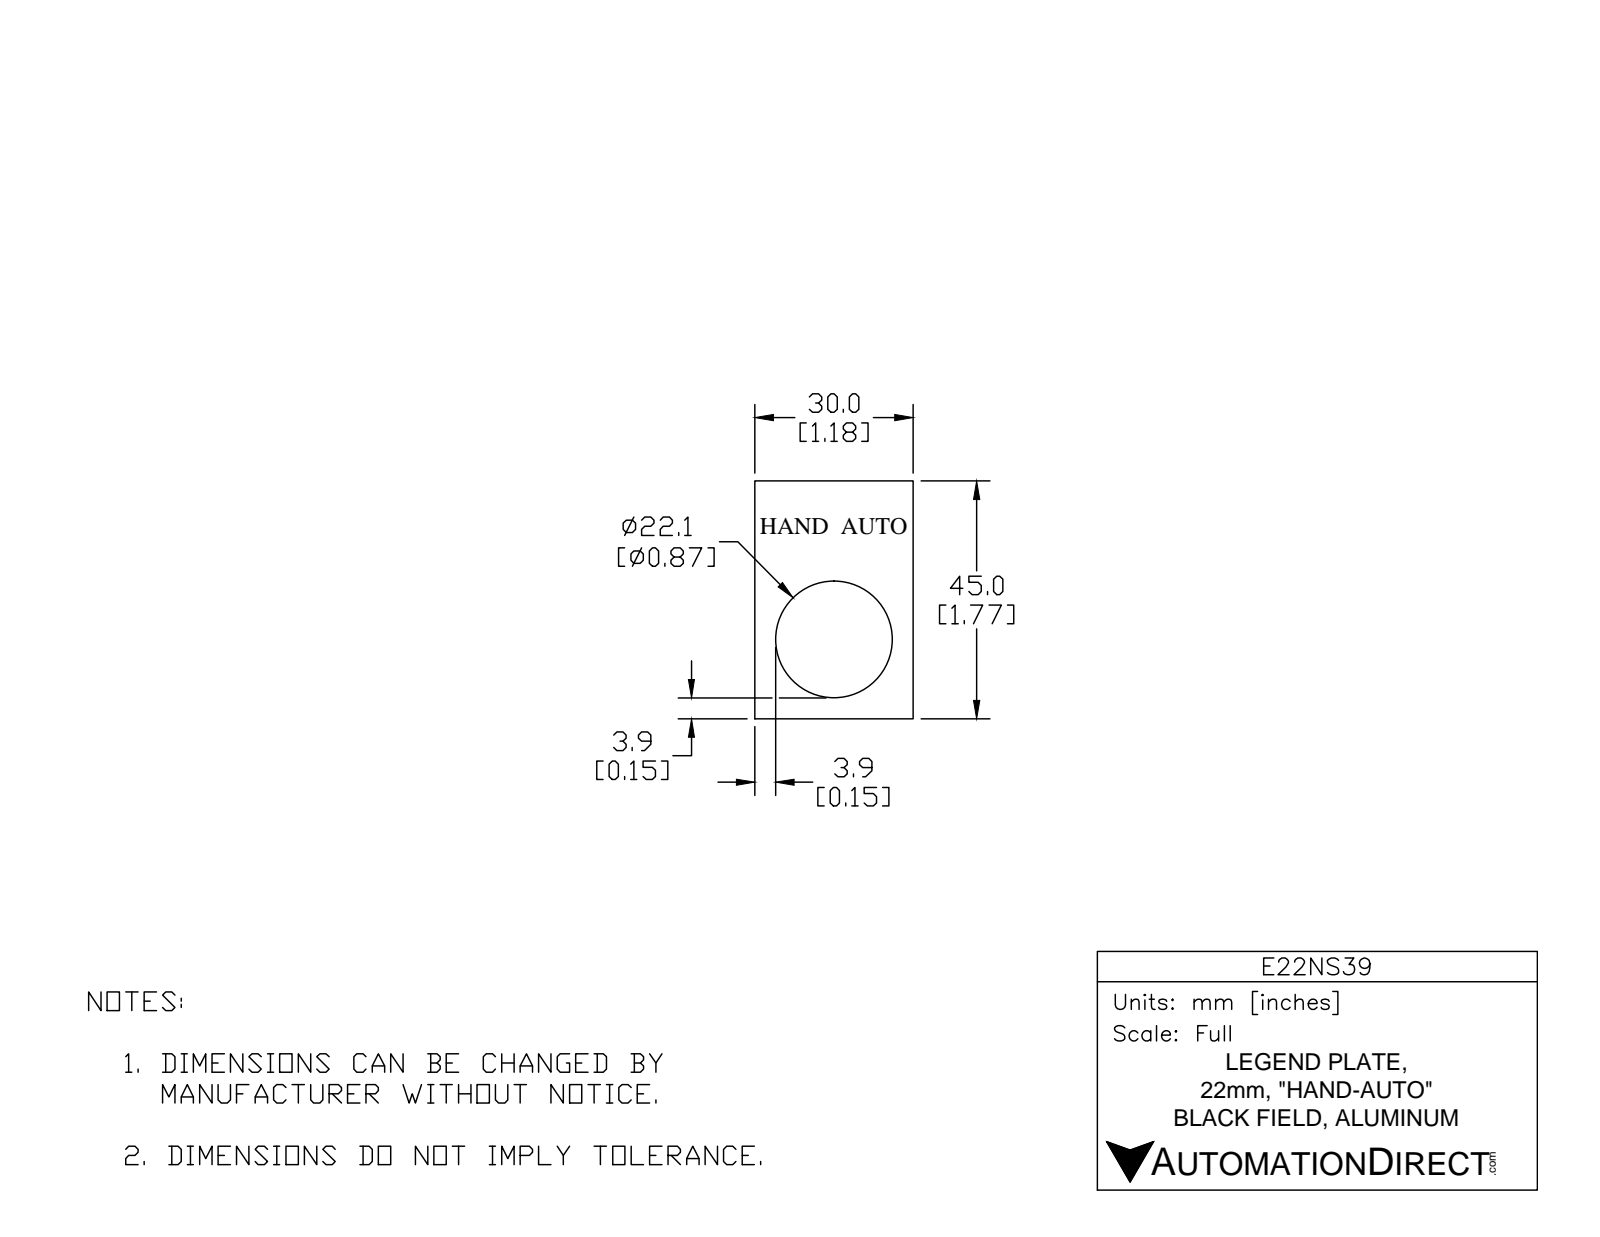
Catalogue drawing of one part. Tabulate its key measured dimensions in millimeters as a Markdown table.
| quantity | value |
| --- | --- |
| part name | E22NS39 |
| STEP written by | SolidWorks 2017 (AUTOMOTIVE_DESIGN) |
| units | millimeters |
| bodies | 1 solid, 115 faces (90 planar, 3 cylindrical, 22 other) |
| overall size | 45 × 30 × 1.3 |
| volume | 1 250 mm³ |
| surface area | 2 251 mm² |
| round holes (diameter × count) | 22.2 × 1 |
| main face-to-face distances | 1.3, 30, 45, 1.05, 4.7, 40.3, 13.4, 16.6, 0.32, 20.84 |
